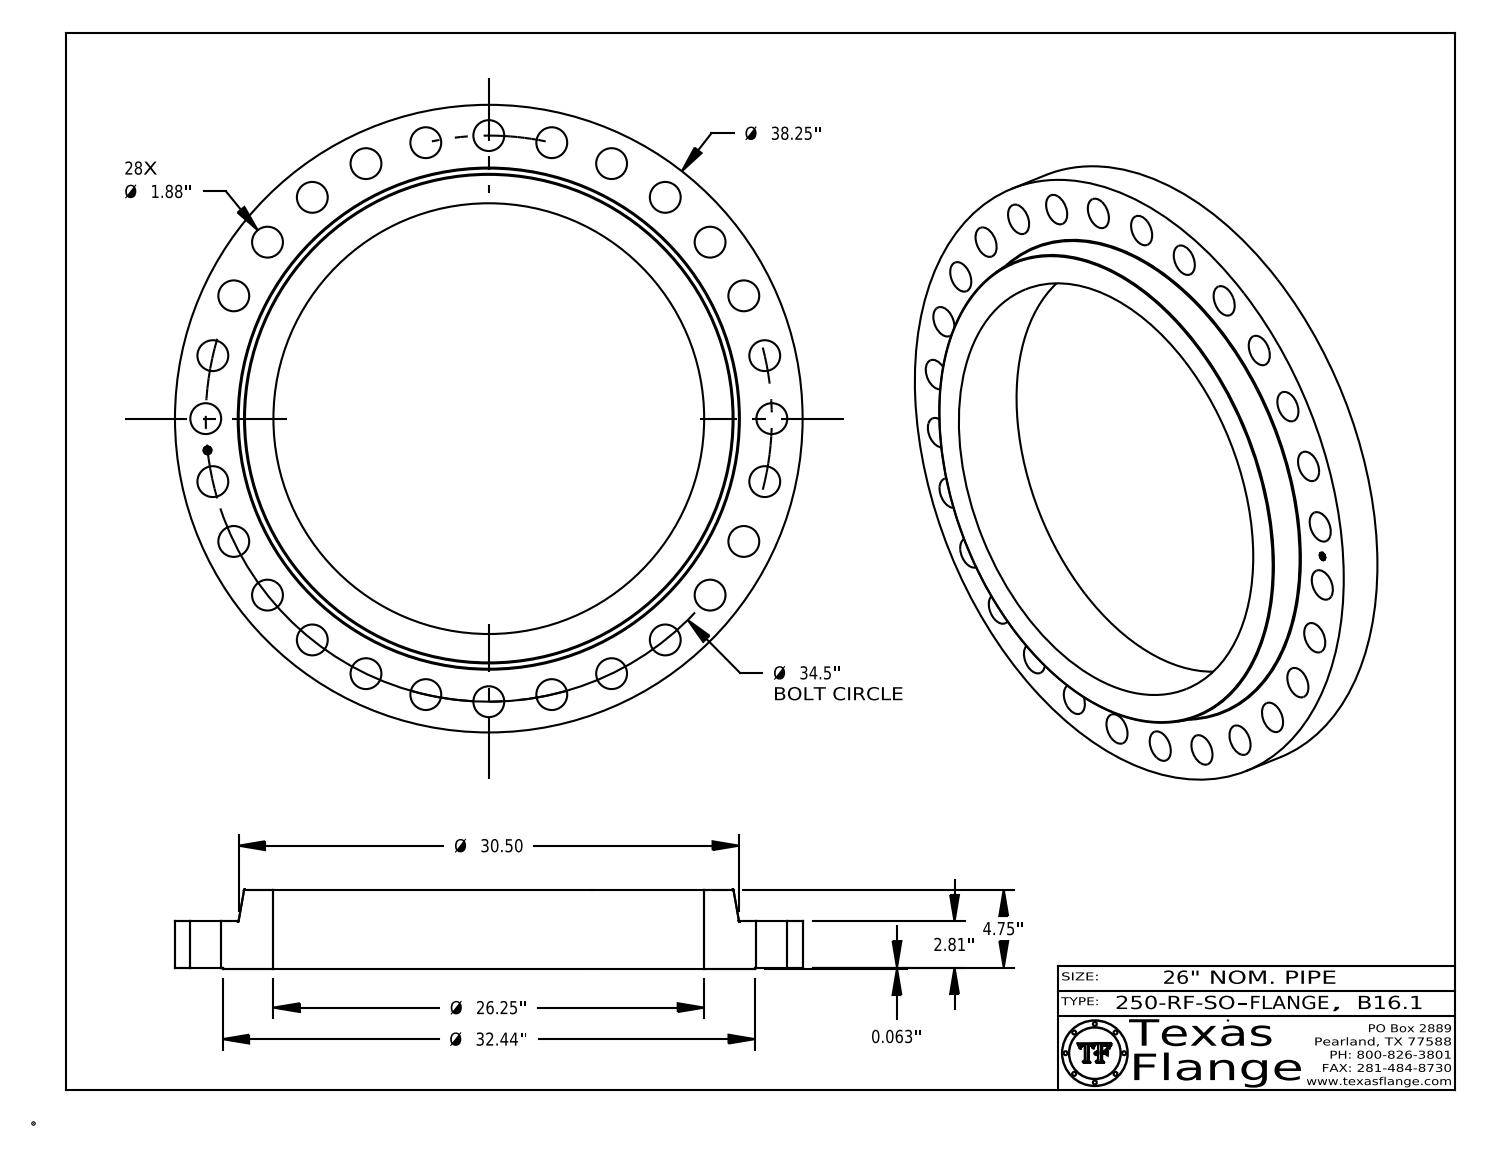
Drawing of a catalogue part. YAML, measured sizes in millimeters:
part_name: "250-RF-SO"
step_written_by: "CATIA V5 STEP AP214 (AUTOMOTIVE_DESIGN)"
units: millimeters
bodies: {solids: 1, faces: 457, planar: 369, cylindrical: 82, other: 6}
overall_size: [971.6, 971.6, 122.3]
volume: 30220000
surface_area: 1559000
round_holes:
  - {diameter: 47.8, count: 28}
  - {diameter: 12.6, count: 1}
  - {diameter: 666.8, count: 1}
round_bosses_or_shafts:
  - {diameter: 0.8, count: 8}
  - {diameter: 971.6, count: 1}
  - {diameter: 824, count: 1}
  - {diameter: 9.9, count: 1}
face_to_face_distances: [72.9, 1.6, 71.4, 122.3, 120.7, 49.3, 72.6, 71, 0.4, 49.7]
hole_center_spacings: [438.2, 685.1, 870.8, 380.2, 466.2, 827.1, 854.3, 289.4]
